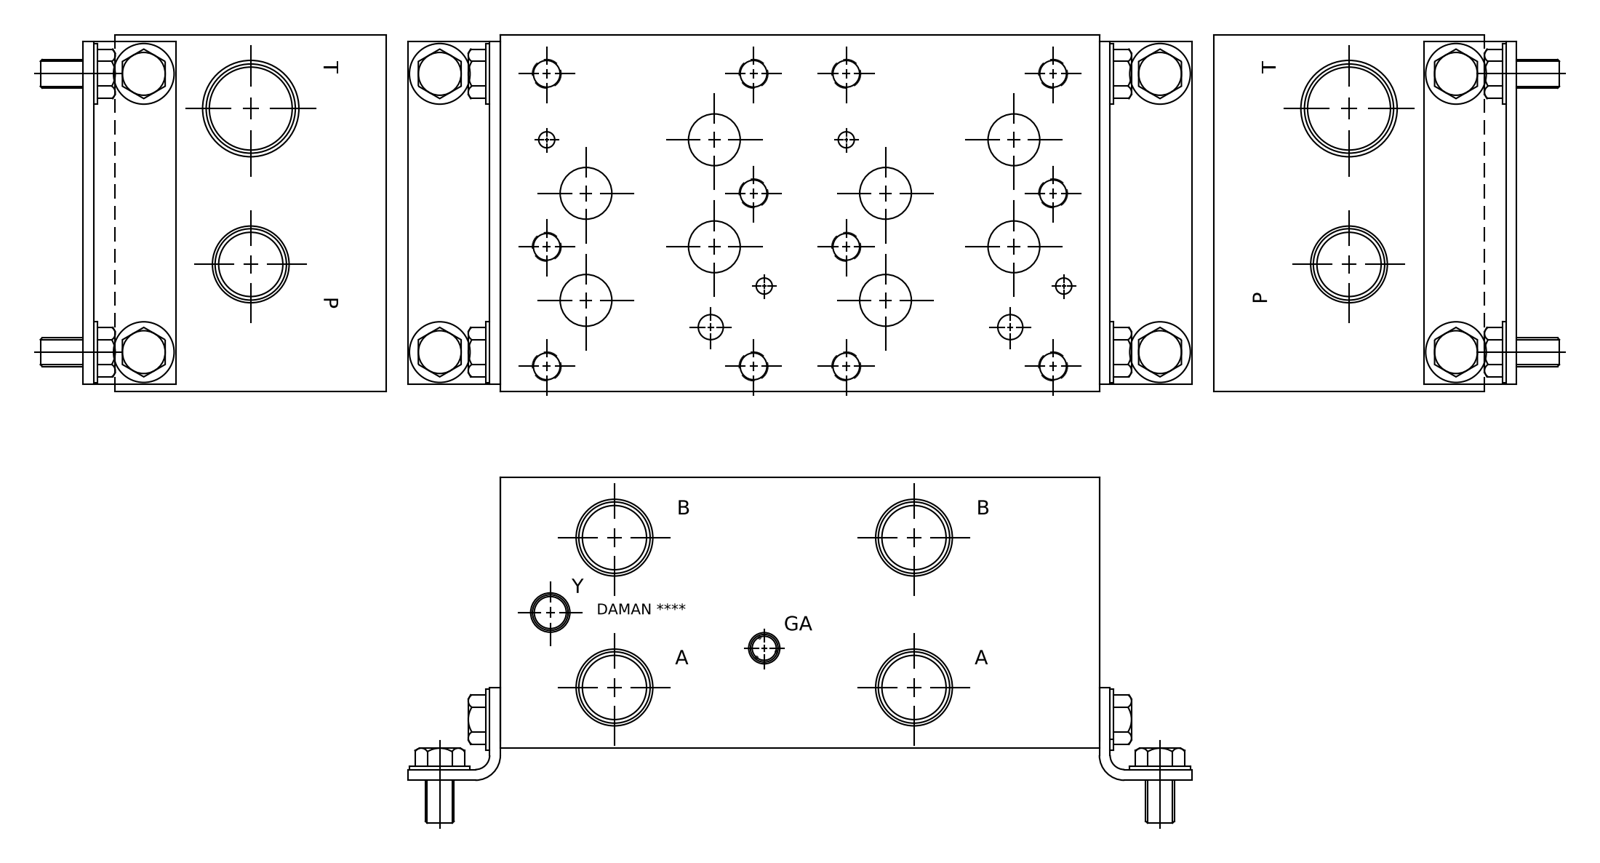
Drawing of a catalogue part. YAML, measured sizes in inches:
part_name: "Part_AD08P025P_3D"
step_written_by: "Autodesk Inventor 2020 (AUTOMOTIVE_DESIGN)"
units: inches
bodies: {solids: 1, faces: 630, planar: 359, cylindrical: 70, other: 201}
overall_size: [10.5, 6.25, 4.75]
volume: 290.3
surface_area: 375.4
round_holes:
  - {diameter: 0.422, count: 15}
  - {diameter: 0.5, count: 14}
  - {diameter: 0.906, count: 7}
  - {diameter: 1.125, count: 5}
  - {diameter: 1.327, count: 5}
  - {diameter: 0.281, count: 4}
  - {diameter: 0.437, count: 1}
  - {diameter: 0.438, count: 1}
  - {diameter: 0.546, count: 1}
  - {diameter: 0.563, count: 1}
  - {diameter: 0.681, count: 1}
  - {diameter: 0.906, count: 1}
face_to_face_distances: [4.75, 6.25, 10.5, 0.748, 5.502, 0.768, 9.732, 9.752, 0.02, 8.984]
hole_center_spacings: [5.25, 1.163, 1.875, 1.163, 2.438, 2.938, 4.221, 1.876]
